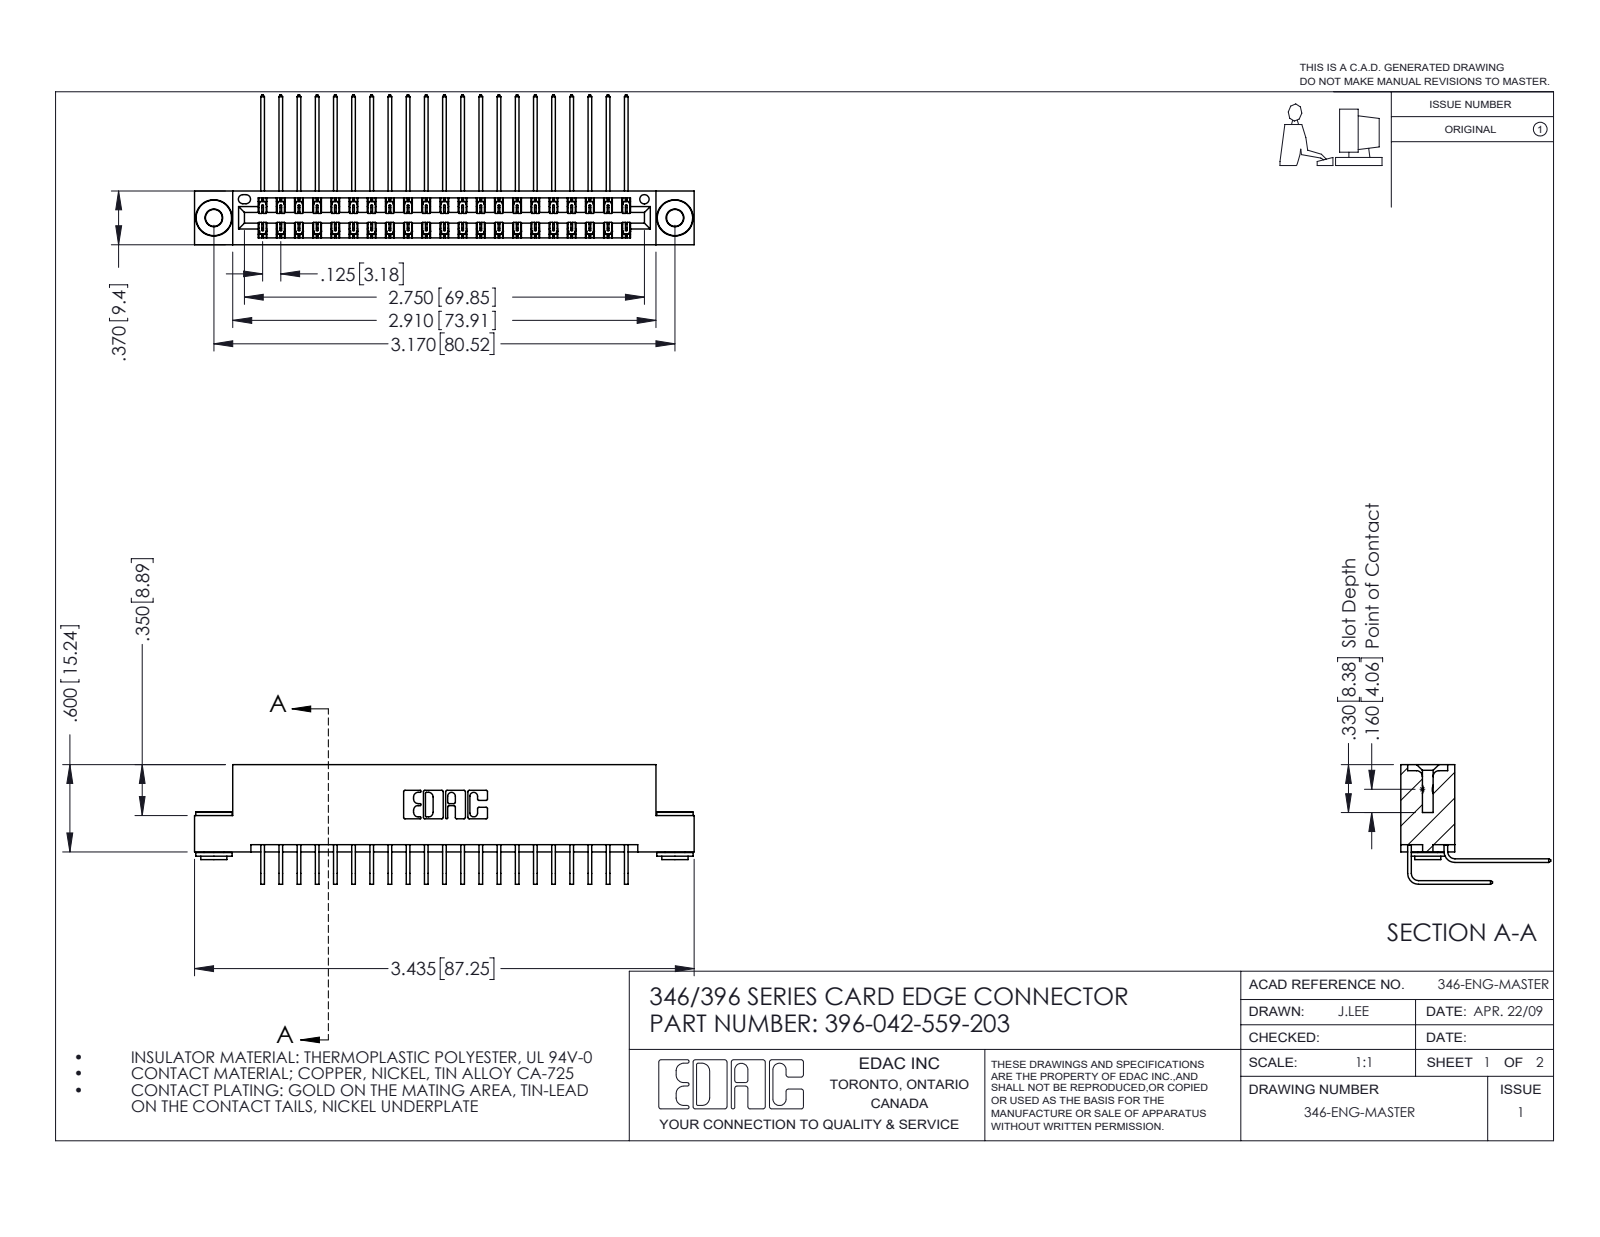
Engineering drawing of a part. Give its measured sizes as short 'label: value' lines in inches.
name: 345-250-002_345-250-002-102; 396-042-559-203; 346 Part_Flush Mounting Lugs - 0.156 Dia-TH; 345-292-001_559 Tail - 2 (+1 more)
written by: SolidWorks 2016 (CONFIG_CONTROL_DESIGN)
unit: in
bodies: 45 solids, 2428 faces (1640 planar, 780 cylindrical, 8 other)
size: 3.435 × 1.03 × 0.823
volume: 0.525 in³; area: 19.96 in²
holes: 2× ⌀0.116, 2× ⌀0.156, 1× ⌀0.064
bosses: 2× ⌀0.25, 2× ⌀0.18, 2× ⌀0.136
rounds: 63× R0.006, 22× R0.01, 6× R0.007, 6× R0.031, 3× R0.026, 2× R0.014, 2× R0.022, 2× R0.024
face distances: 0.048, 0.322, 0.25, 0.025, 0.37, 0.072, 0.298, 0.275, 0.148, 0.222
hole spacings: 0.246, 2.963, 3.17
